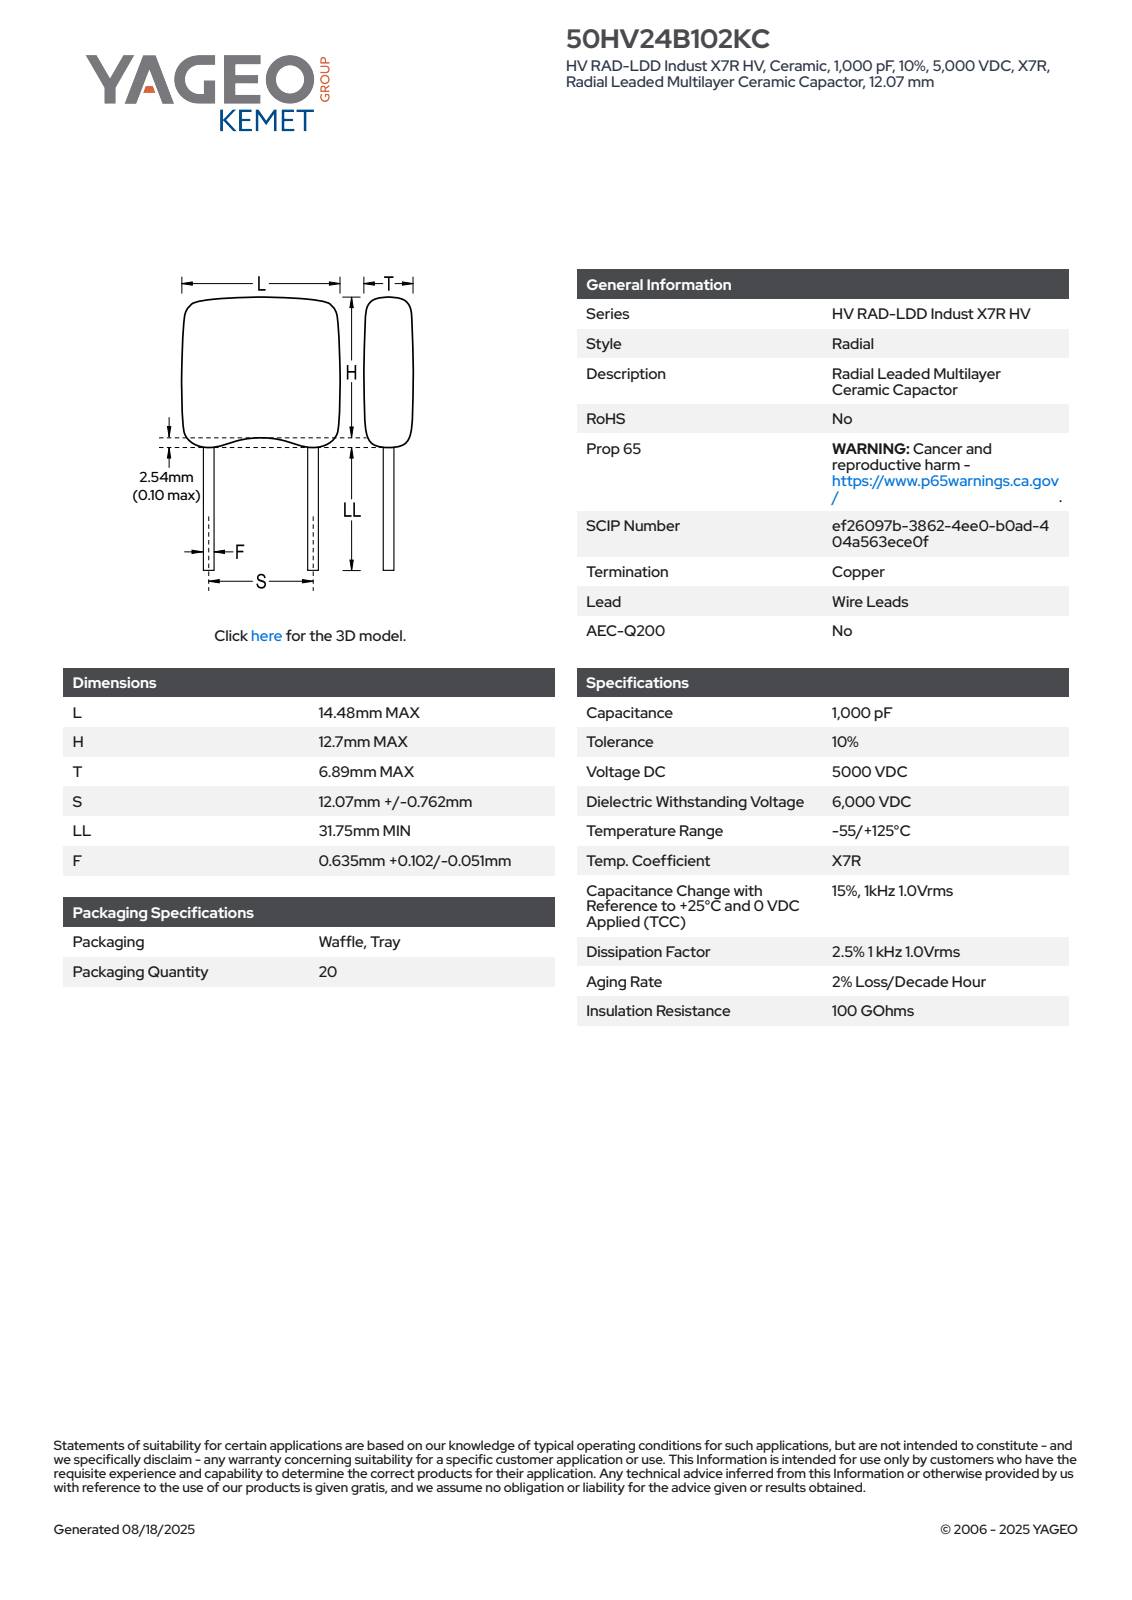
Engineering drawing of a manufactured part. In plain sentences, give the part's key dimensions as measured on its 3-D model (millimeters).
The part is named "CCRM_RCST_HV24_L14.48H12.7T6.89S12.07LL31.75F0.737". Its 3-D file was written by "SolidWorks 2021 (AUTOMOTIVE_DESIGN)". It is 4 solids with 98 faces: 66 planar, 20 cylindrical and 12 other. Overall it measures 17.45 by 14.48 by 6.89 millimeters. Its volume is 1 308 cubic millimeters and its surface area 774 square millimeters. Round bosses or shafts: 2 of diameter 0.74. Partial cylindrical surfaces (rounded edges, fillets, slot ends): 8 of radius 1, 4 of radius 0.5. The main face-to-face distances are 6.89, 14.48, 14.28, 3.17, 17.45, 11.34, 8.17, 6.11, 9.5, 6.33.
